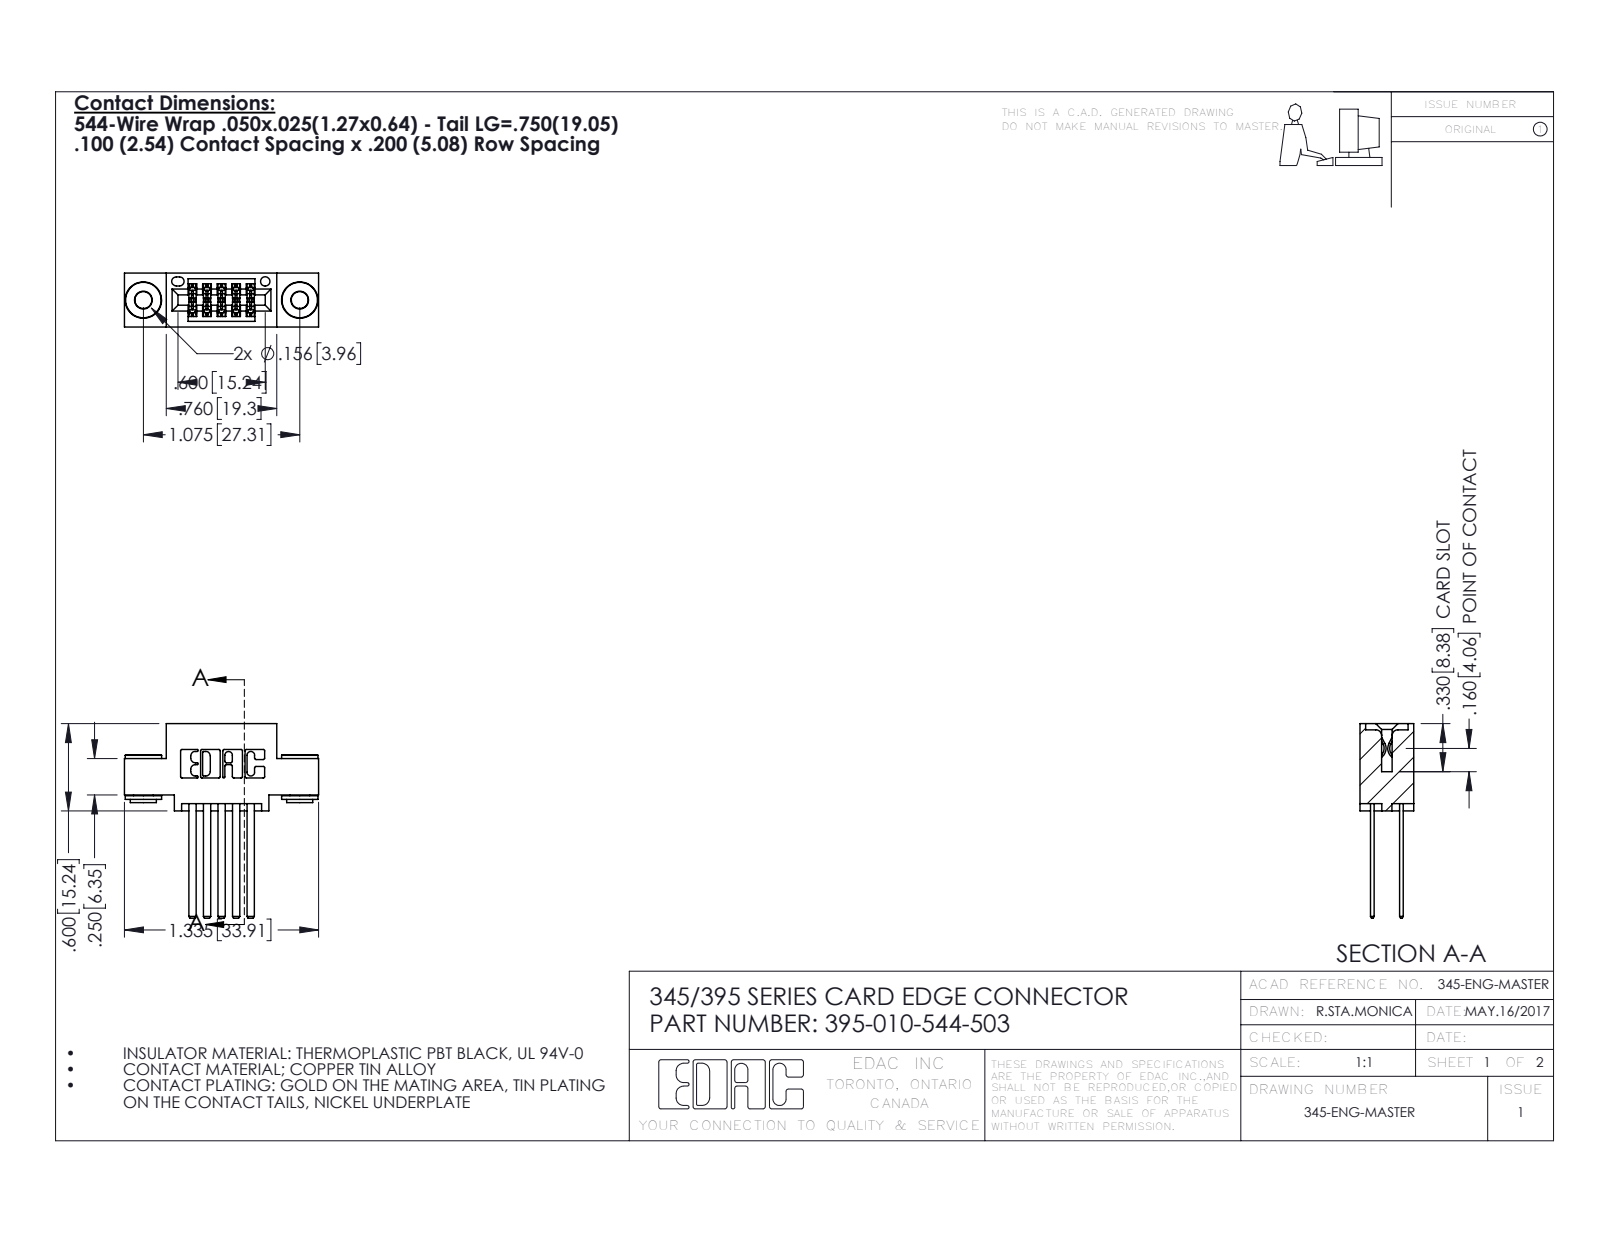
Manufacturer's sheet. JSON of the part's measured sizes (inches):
{"part_name": "345 Part_0.110 Offset - 0.156 Dia-TH; 345-292-001_345-293-144; 395-010-544-503; 345-250-002_345-250-002-102", "step_written_by": "SolidWorks 2016 (CONFIG_CONTROL_DESIGN)", "units": "inches", "bodies": {"solids": 13, "faces": 608, "planar": 384, "cylindrical": 216, "other": 8}, "overall_size": [1.337, 1.335, 0.37], "volume_in3": 0.185, "surface_area_in2": 6.945, "round_holes": [[0.116, 2], [0.156, 2], [0.064, 1]], "round_bosses_or_shafts": [[0.25, 2], [0.18, 2], [0.136, 2]], "partial_cylinders_radius": [[0.01, 22], [0.006, 15], [0.007, 6], [0.031, 6], [0.026, 3], [0.014, 2], [0.019, 2], [0.022, 2]], "face_to_face_distances": [0.2, 0.072, 0.298, 0.025, 0.098, 0.272, 0.05, 0.15, 0.1, 0.25], "hole_center_spacings": [0.27, 0.847, 1.075]}
